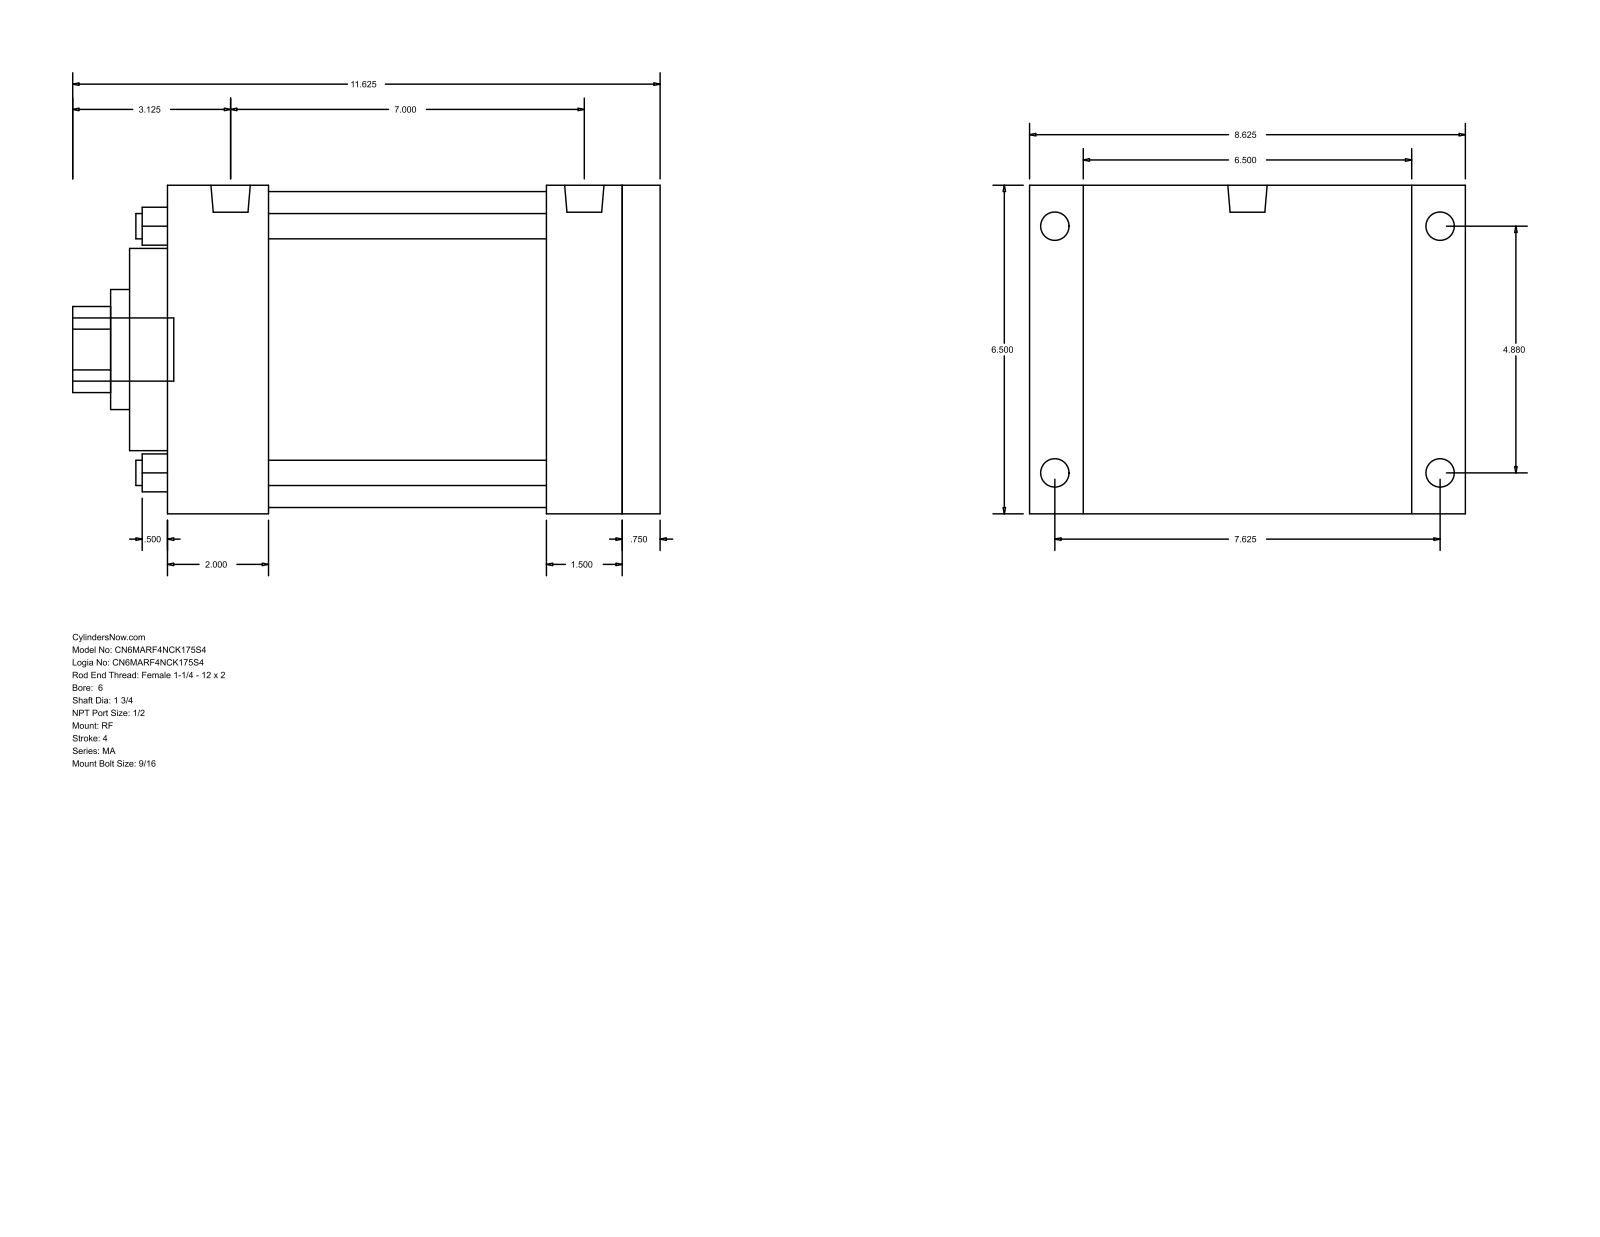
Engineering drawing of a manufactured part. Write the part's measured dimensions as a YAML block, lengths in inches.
part_name: "MA_RF__0600_1.75"
step_written_by: "GSSL Pune (CONFIG_CONTROL_DESIGN)"
units: inches
bodies: {solids: 0, faces: 94, planar: 65, cylindrical: 29, other: 0}
overall_size: [11.625, 8.625, 6.5]
round_holes:
  - {diameter: 0.5, count: 4}
  - {diameter: 1.75, count: 1}
  - {diameter: 2.375, count: 1}
  - {diameter: 4, count: 1}
  - {diameter: 6.25, count: 1}
round_bosses_or_shafts:
  - {diameter: 0.687, count: 4}
  - {diameter: 0.563, count: 4}
  - {diameter: 0.778, count: 2}
  - {diameter: 1.25, count: 1}
partial_cylinders:
  - {radius: 0.852, count: 1}
face_to_face_distances: [6.5, 9.75, 0.75, 9, 0.75, 2, 7, 7.75, 7.5, 5.5]
hole_center_spacings: [3.451, 4.88, 6.902]
